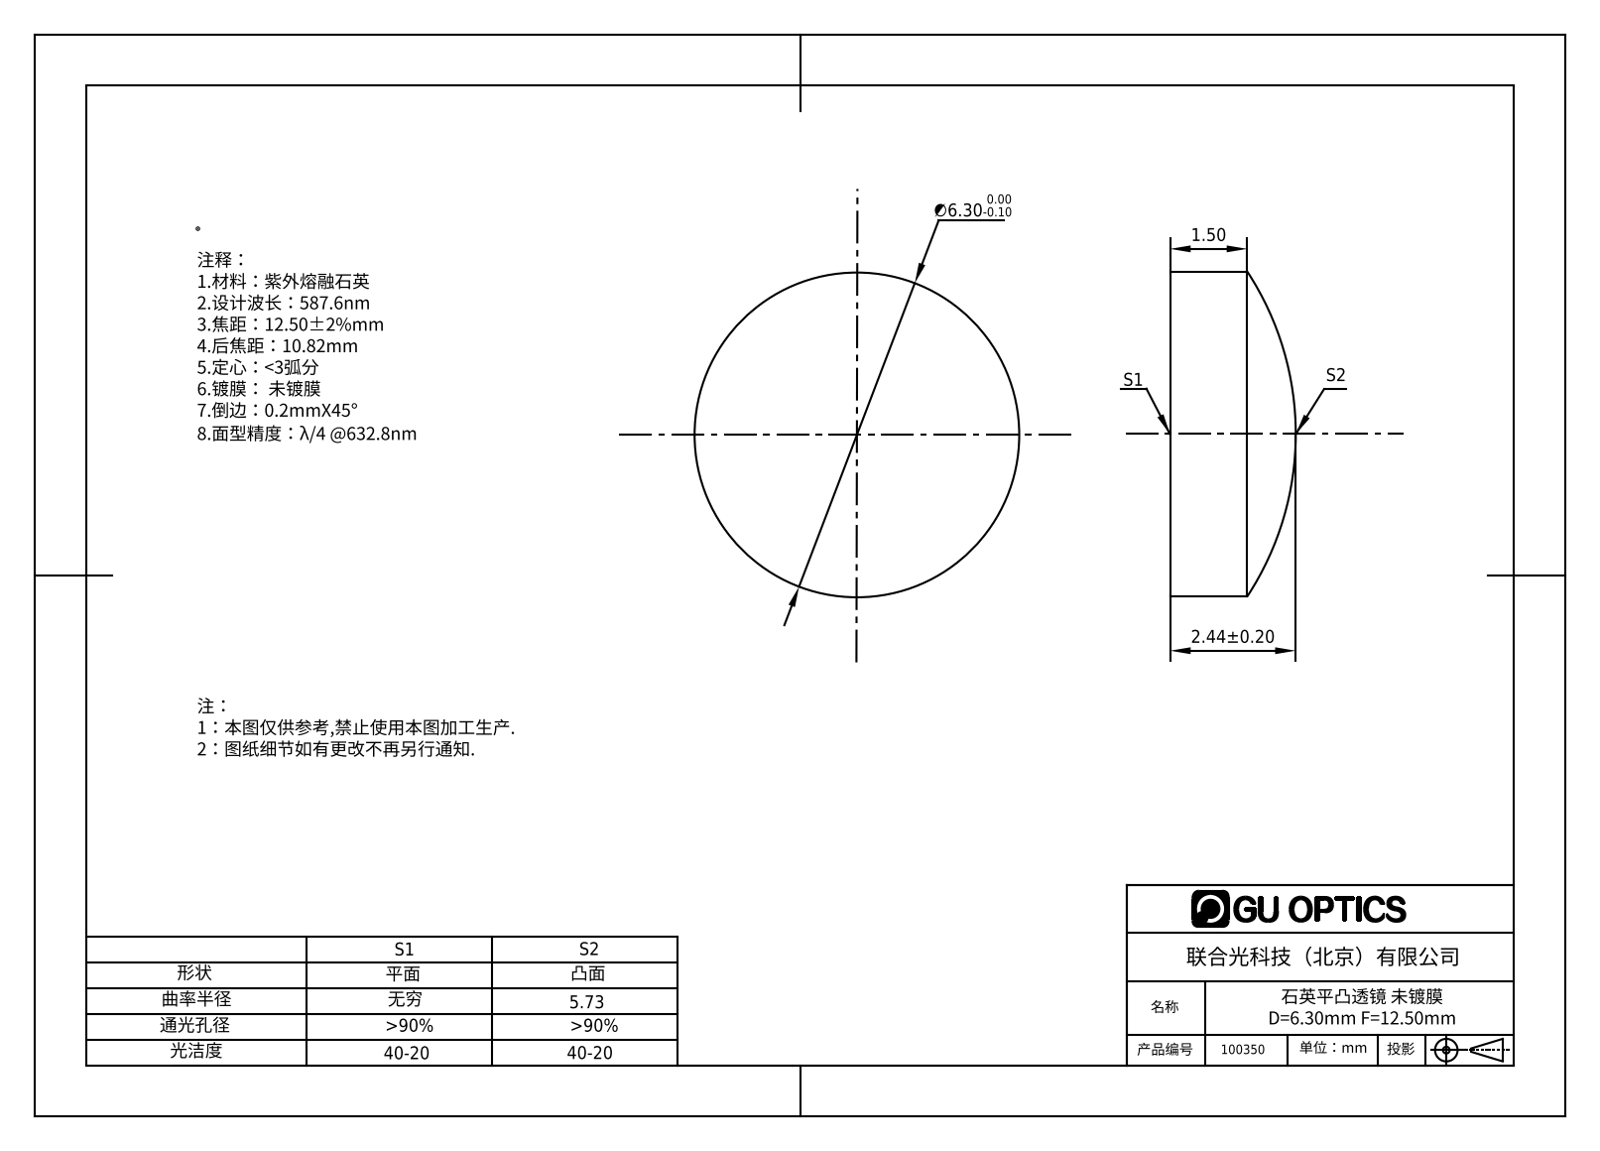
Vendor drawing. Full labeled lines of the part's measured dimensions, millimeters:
Part name (STEP PRODUCT): 100350
STEP written by: SolidWorks 2016 (AUTOMOTIVE_DESIGN)
Units: millimetres
Bodies: 1 solid, 5 faces (1 planar, 2 cylindrical, 2 other)
Overall size (bounding box): 6.3 × 6.3 × 2.44
Volume: 62 mm³ · Surface area: 95 mm²
Round bosses / shafts (diameter × count): ⌀6.3 ×1
